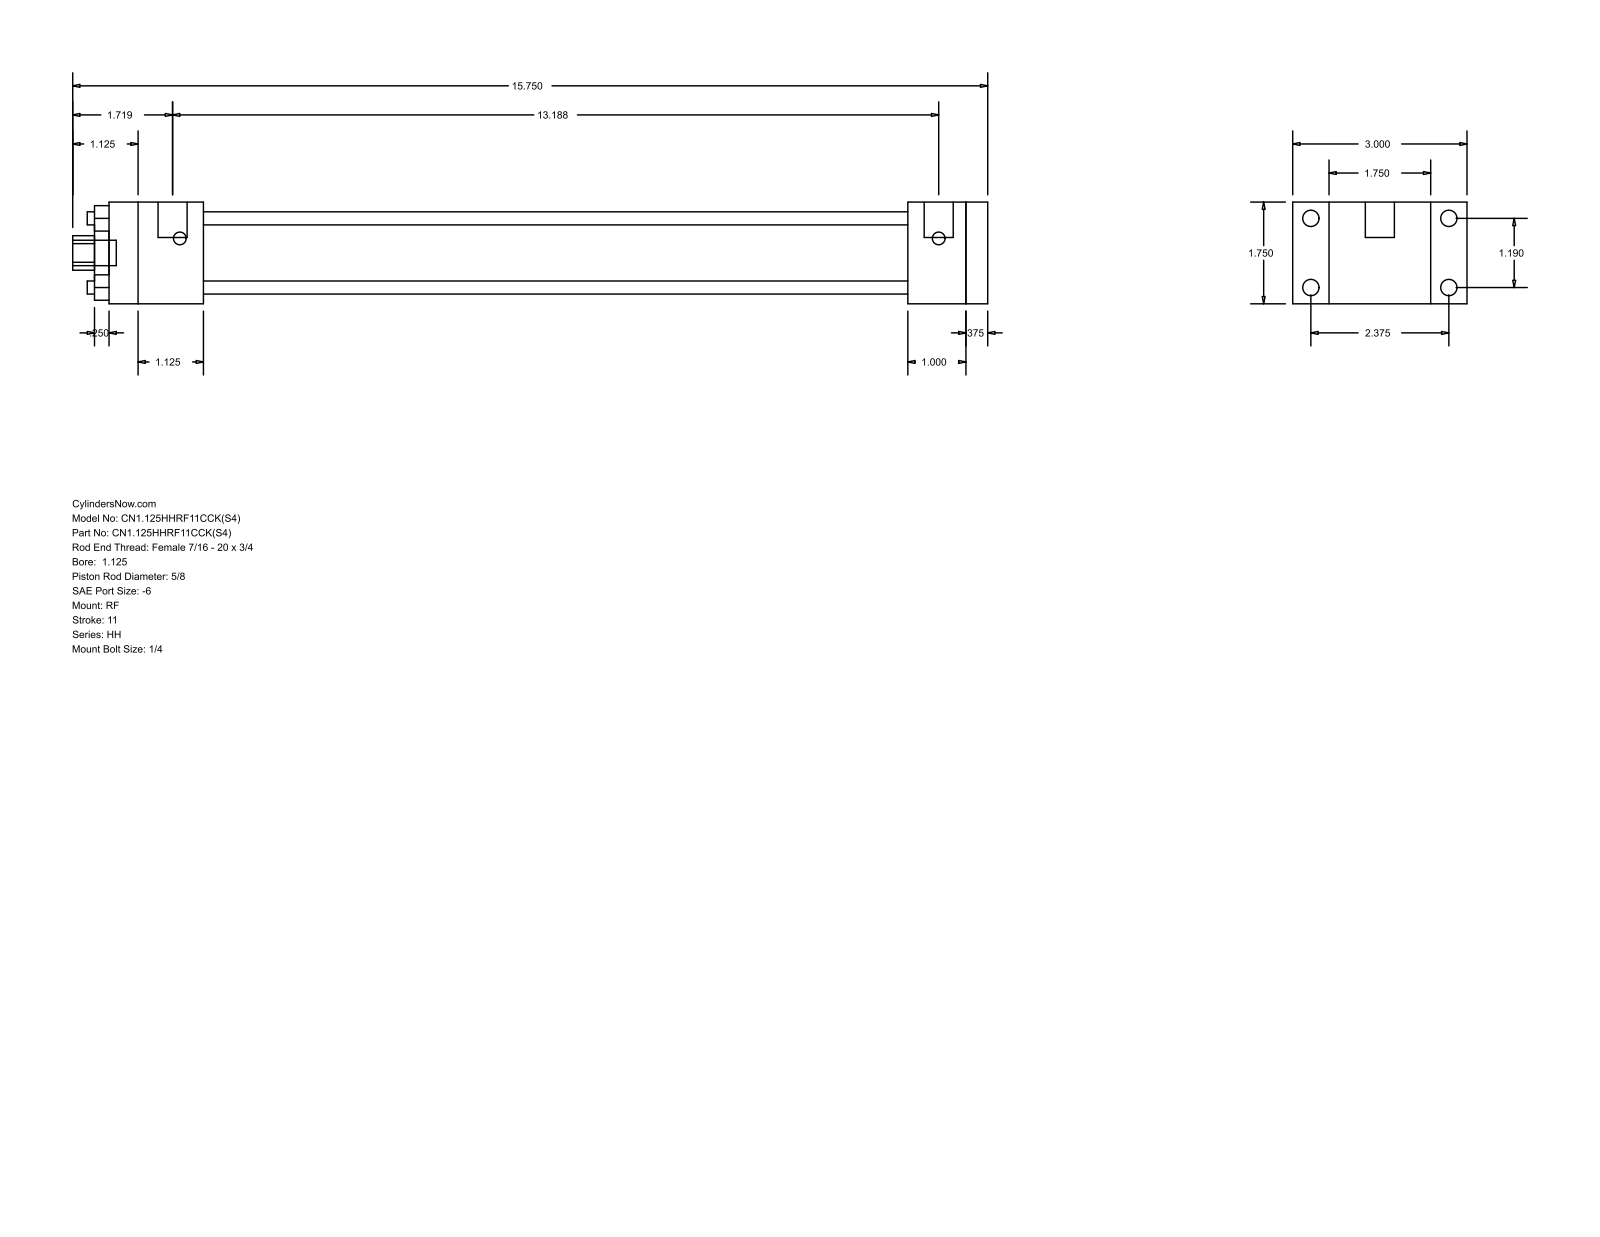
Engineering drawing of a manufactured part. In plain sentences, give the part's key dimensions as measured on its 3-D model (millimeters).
The part is named "HH_RF__0112_0.625". Its 3-D file was written by "GSSL Pune (CONFIG_CONTROL_DESIGN)". It is 0 solids with 92 faces: 64 planar, 28 cylindrical and 0 other. Overall it measures 400.05 by 76.2 by 44.45 millimeters. Round holes: 4 of diameter 5.71, 1 of diameter 15.88, 1 of diameter 28.57, 1 of diameter 34.92. Round bosses or shafts: 4 of diameter 7.14, 4 of diameter 5.56, 2 of diameter 12.7, 1 of diameter 11.11. Partial cylindrical surfaces (rounded edges, fillets, slot ends): 1 of radius 7.54. The main face-to-face distances are 44.46, 9.53, 384.17, 15.87, 333.37, 342.9, 307.97, 25.4, 34.93, 41.27. The hole center spacings are 21.37, 30.22, 42.74.
